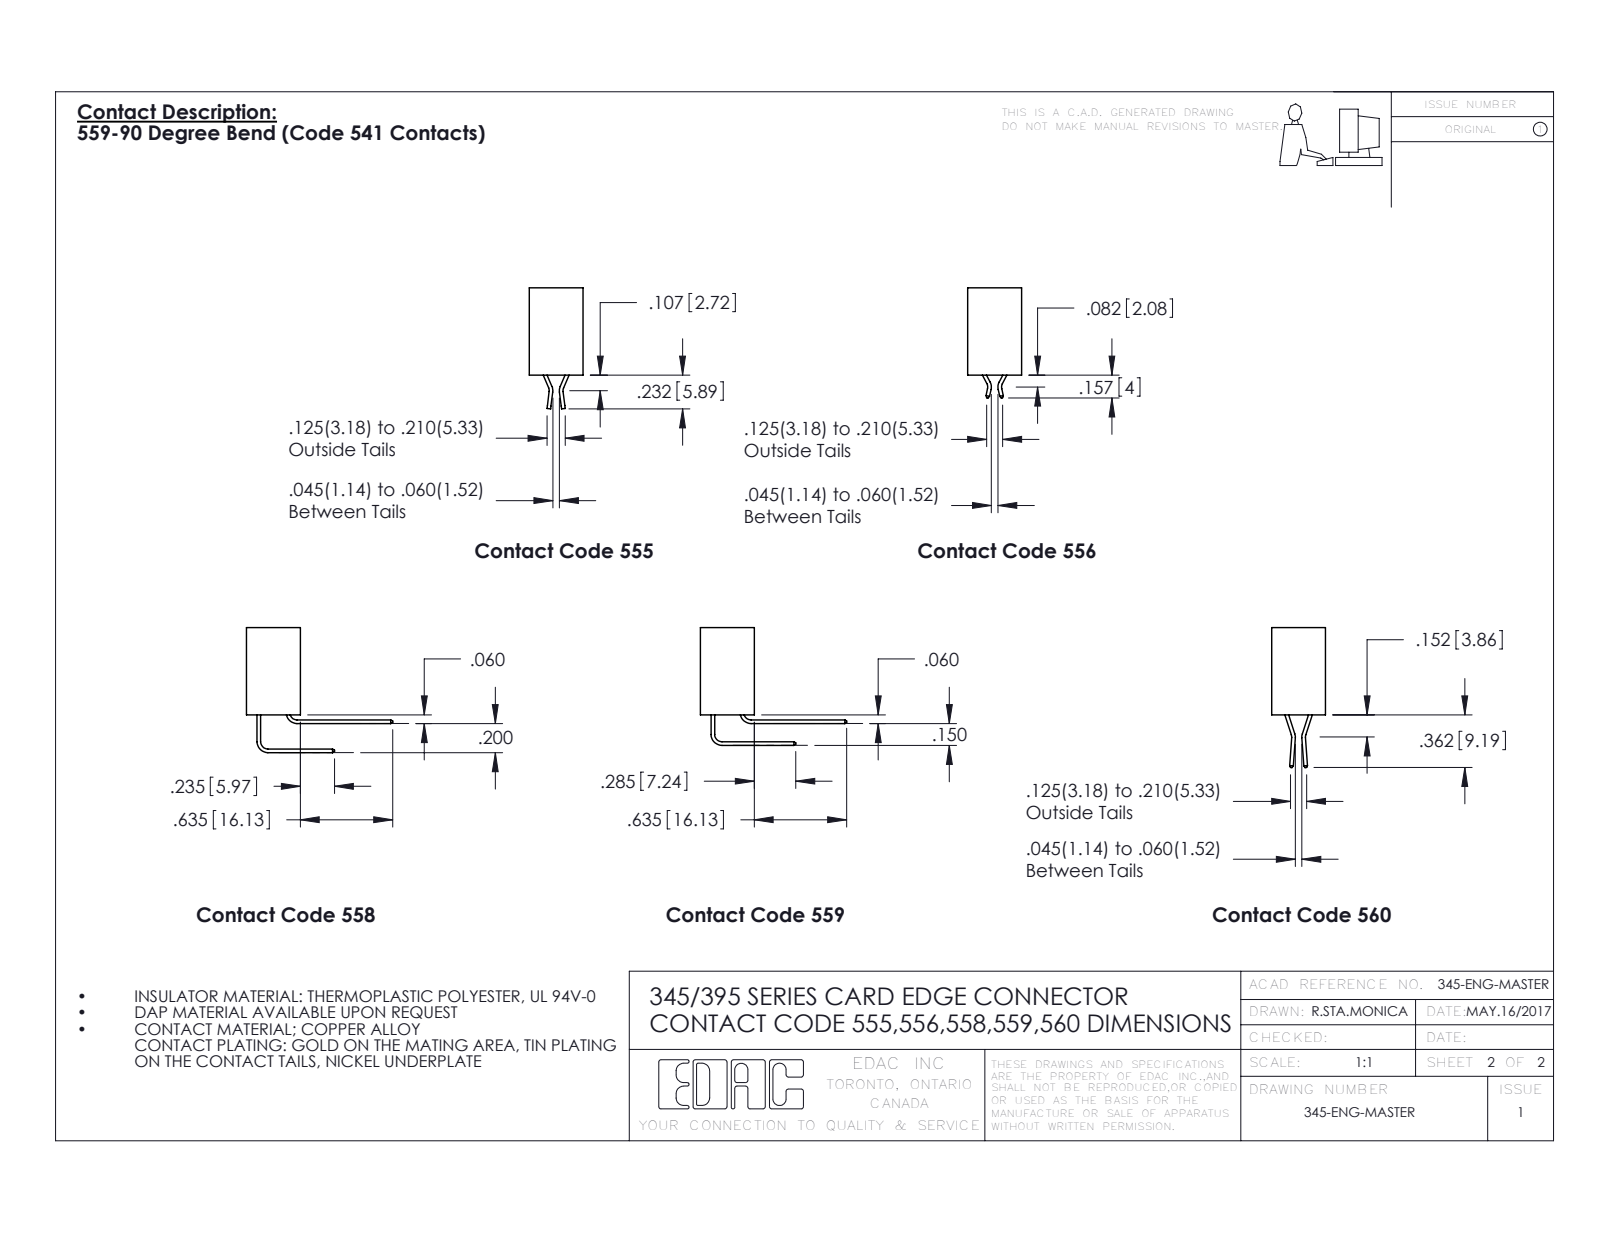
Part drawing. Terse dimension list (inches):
name: 345 Part_0.110 Offset - Side Mount; 395-050-556-512; 345-292-001_556 Tail
written by: SolidWorks 2016 (CONFIG_CONTROL_DESIGN)
unit: in
bodies: 51 solids, 2930 faces (1934 planar, 996 cylindrical, 0 other)
size: 3.335 × 0.757 × 0.37
volume: 0.483 in³; area: 17.47 in²
holes: 2× ⌀0.128, 1× ⌀0.064
rounds: 75× R0.006, 22× R0.01, 6× R0.007, 6× R0.031, 3× R0.026, 2× R0.01, 2× R0.014, 2× R0.019
face distances: 0.298, 0.072, 0.2, 0.37, 0.025, 0.098, 0.272, 0.225, 0.175, 0.149
hole spacings: 3.075
